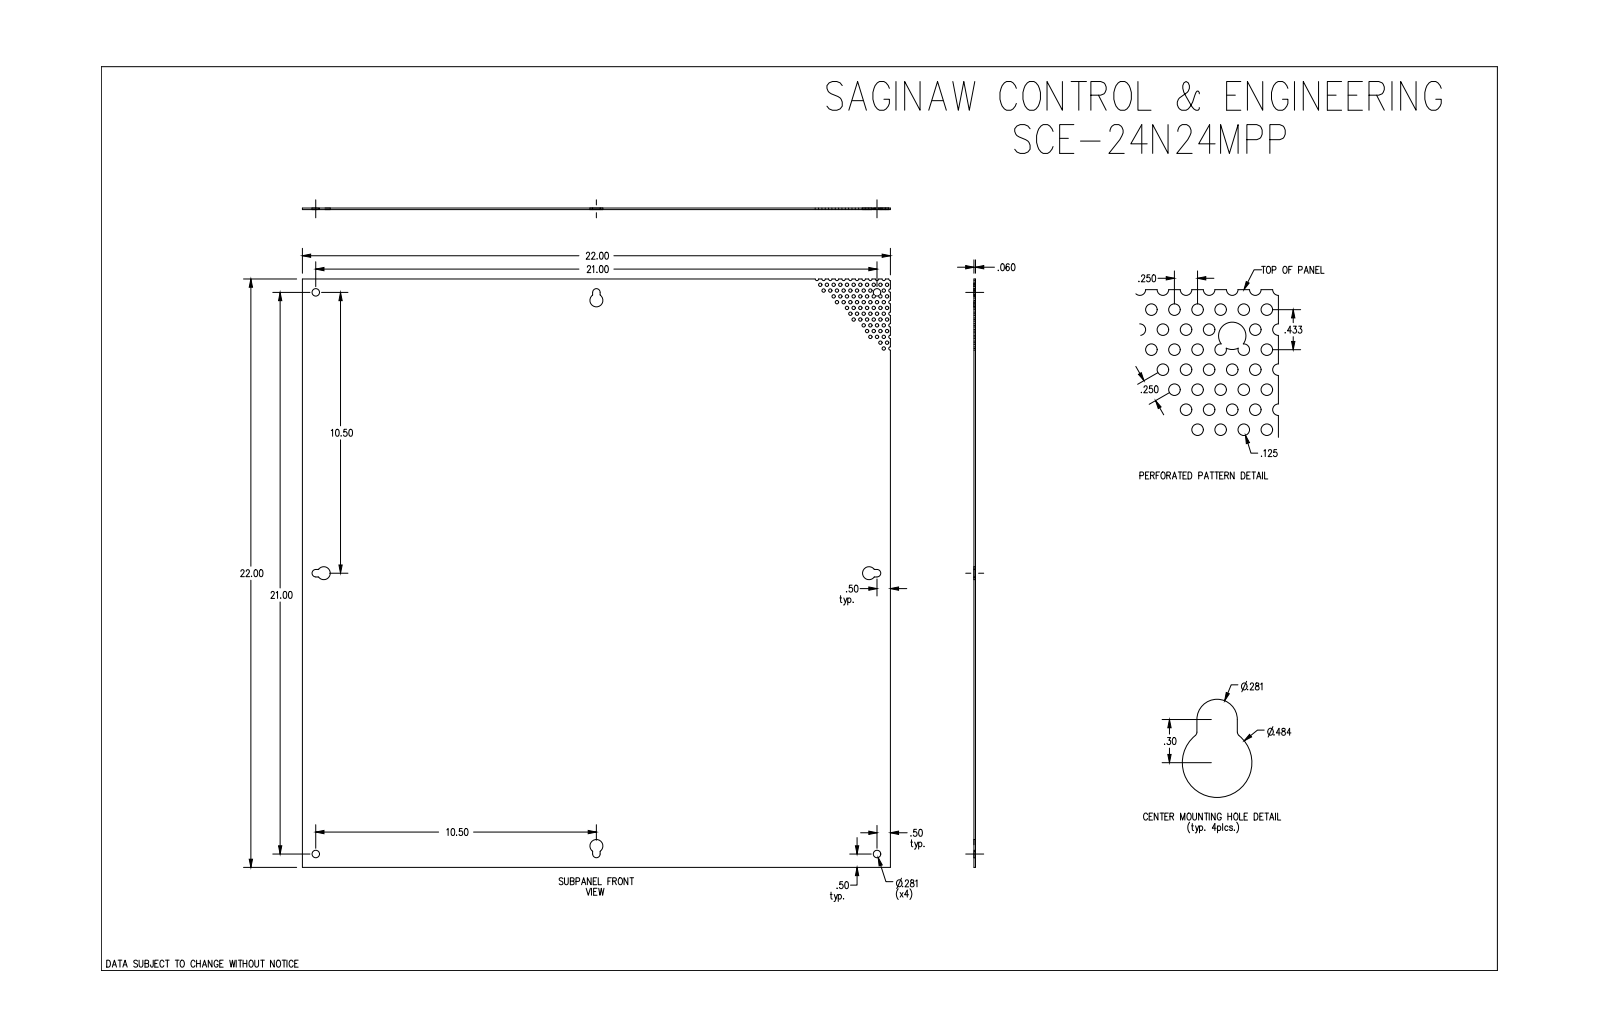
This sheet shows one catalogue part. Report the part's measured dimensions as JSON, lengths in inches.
{"part_name": "SCE-24N24MPP", "step_written_by": "SolidWorks 2019 (CONFIG_CONTROL_DESIGN)", "units": "inches", "bodies": {"solids": 1, "faces": 140, "planar": 31, "cylindrical": 109, "other": 0}, "overall_size": [22, 22, 0.06], "volume_in3": 28.91, "surface_area_in2": 971.3, "round_holes": [[0.125, 45], [0.125, 25], [0.281, 4]], "partial_cylinders_radius": [[0.063, 11], [0.03, 8], [0.062, 7], [0.141, 4], [0.242, 4]], "face_to_face_distances": [0.06, 22, 10.859, 11.141, 0.281], "hole_center_spacings": [0.25, 0.661, 0.5, 0.433, 1.323, 0.433, 1.09, 0.75]}
